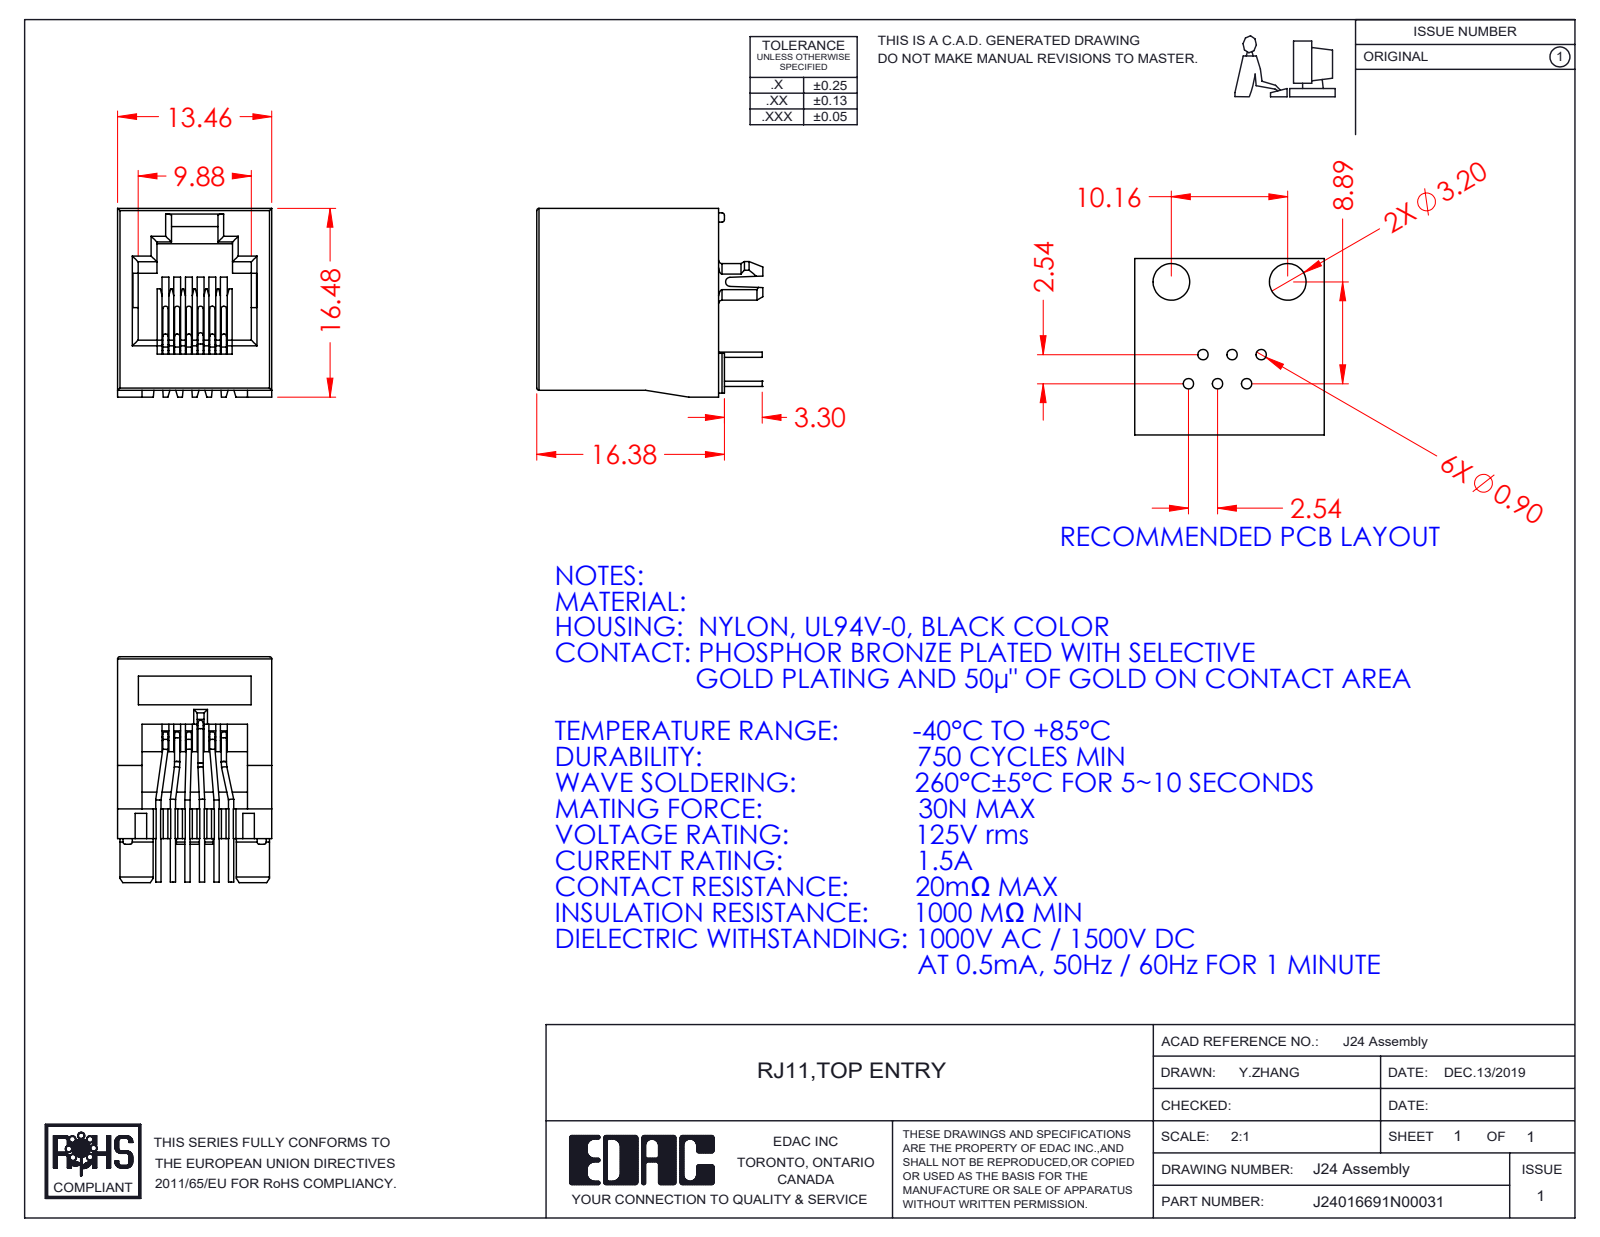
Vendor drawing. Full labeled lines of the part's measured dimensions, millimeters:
Part name (STEP PRODUCT): RJ24016691N00071; 24 Contacts_MBB; 24 Insulator_MBB
STEP written by: SolidWorks 2016 (CONFIG_CONTROL_DESIGN)
Units: millimetres
Bodies: 7 solids, 450 faces (262 planar, 152 cylindrical, 36 other)
Overall size (bounding box): 19.73 × 16.48 × 13.46
Volume: 1 746 mm³ · Surface area: 2 940 mm²
Round holes (diameter × count): ⌀0.46 ×6, ⌀2.1 ×2
Round bosses / shafts (diameter × count): ⌀0.46 ×27
Partial cylindrical surfaces — rounded edges, fillets, slot ends (radius × count): R0.5 ×18, R0.2 ×10, R0.32 ×6, R0.34 ×6, R0.25 ×3, R1.6 ×2, R1.77 ×2, R0.4 ×1
Main face-to-face distances: 13.46, 1.02, 1.79, 11.67, 2.04, 0.6, 15.87, 8.24, 3.43, 10.03
Hole centre spacings: 2.84, 2.54, 4.58, 5.08, 13.1, 6.84, 10.16, 10.35
